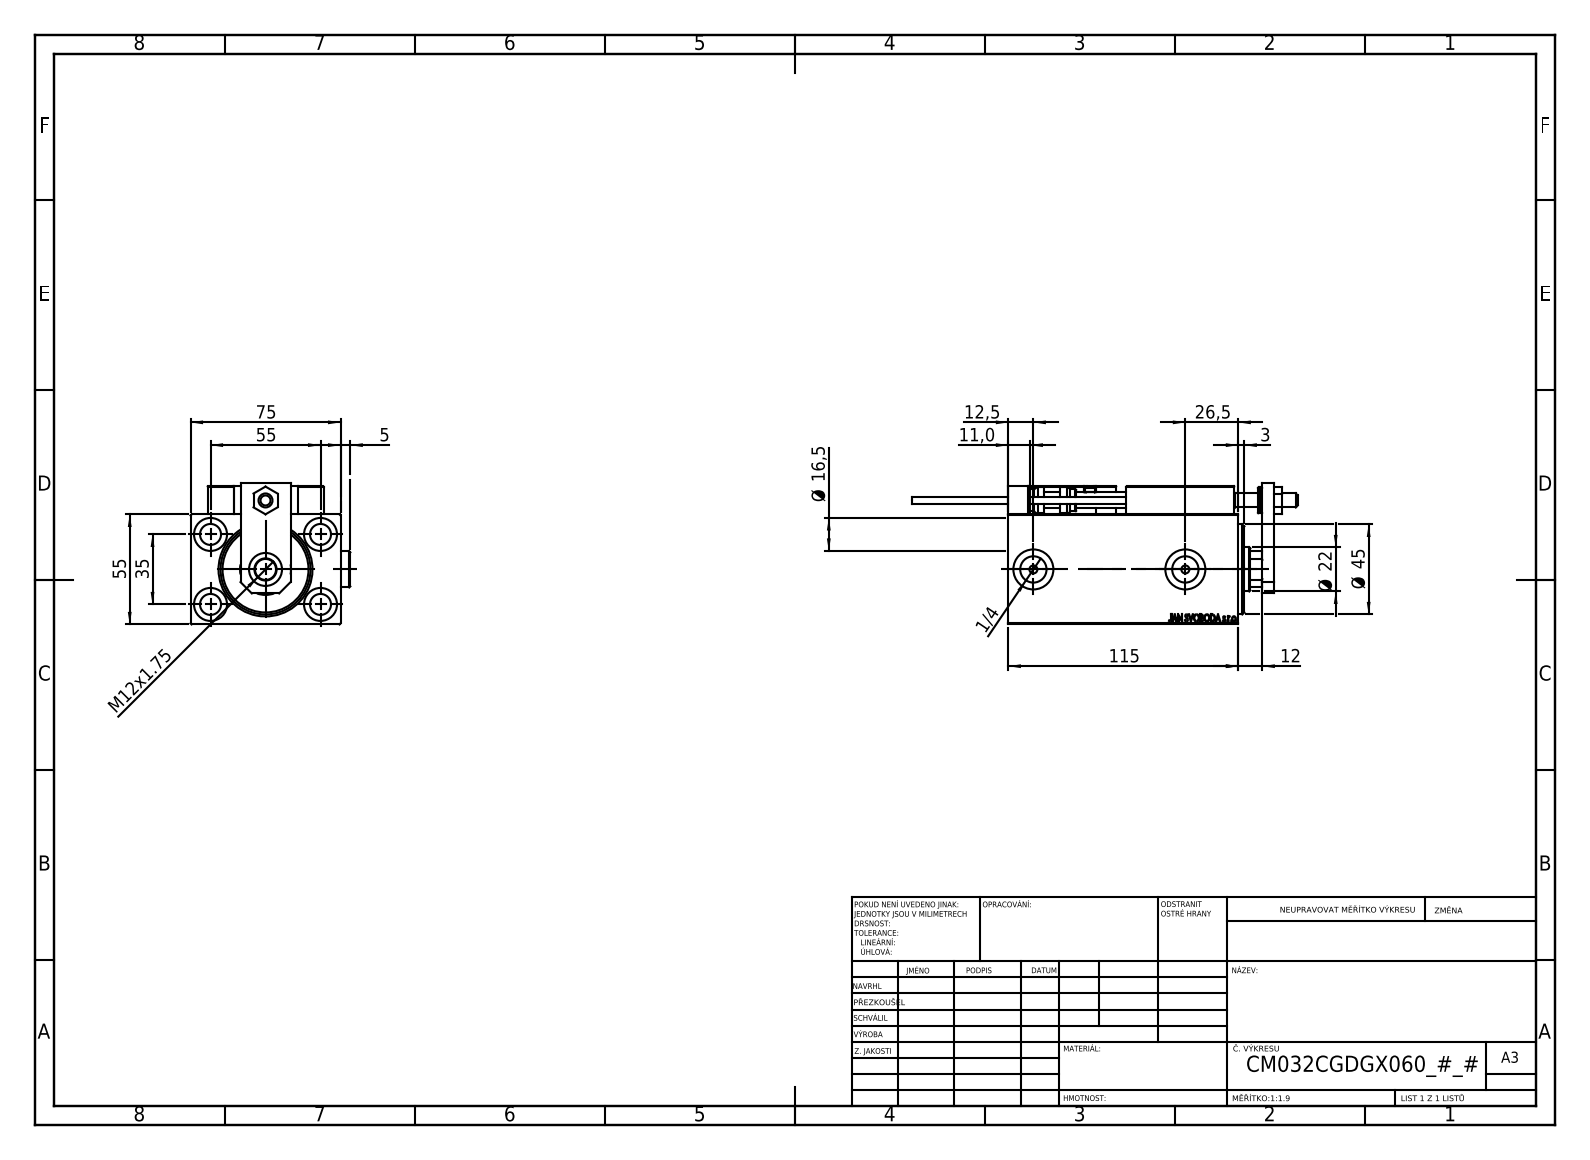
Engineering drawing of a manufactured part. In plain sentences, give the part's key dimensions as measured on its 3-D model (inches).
The part is named "ALLEN BOLT D5; SWITCH_X_FRONT_BACK; NUT_D12; V450CM_C_VCP (+7 more)". Its 3-D file was written by "SolidWorks 2019 (CONFIG_CONTROL_DESIGN)". It is 25 solids with 1336 faces: 594 planar, 204 cylindrical and 538 other. Overall it measures 7.587 by 3.146 by 2.776 inches. Its volume is 27.33 cubic inches and its surface area 171.8 square inches. Round holes: 6 of diameter 0.157, 5 of diameter 0.315, 5 of diameter 0.413, 5 of diameter 0.65, 4 of diameter 0.126, 2 of diameter 0.197, 2 of diameter 0.518, 2 of diameter 0.787, 1 of diameter 0.276, 1 of diameter 0.866, 1 of diameter 1.004, 1 of diameter 1.26. Round bosses or shafts: 2 of diameter 0.709, 2 of diameter 0.197, 2 of diameter 0.15, 1 of diameter 0.512, 1 of diameter 0.433. Partial cylindrical surfaces (rounded edges, fillets, slot ends): 30 of radius 0.012, 2 of radius 0.118, 1 of radius 0.413. The main face-to-face distances are 2.165, 2.953, 0.551, 0.394, 0.472, 0.197, 2.717, 0.276, 0.591, 0.984. The hole center spacings are 1.283, 0.448, 0.787, 1.165, 1.169, 1.273, 1.378, 1.42.
